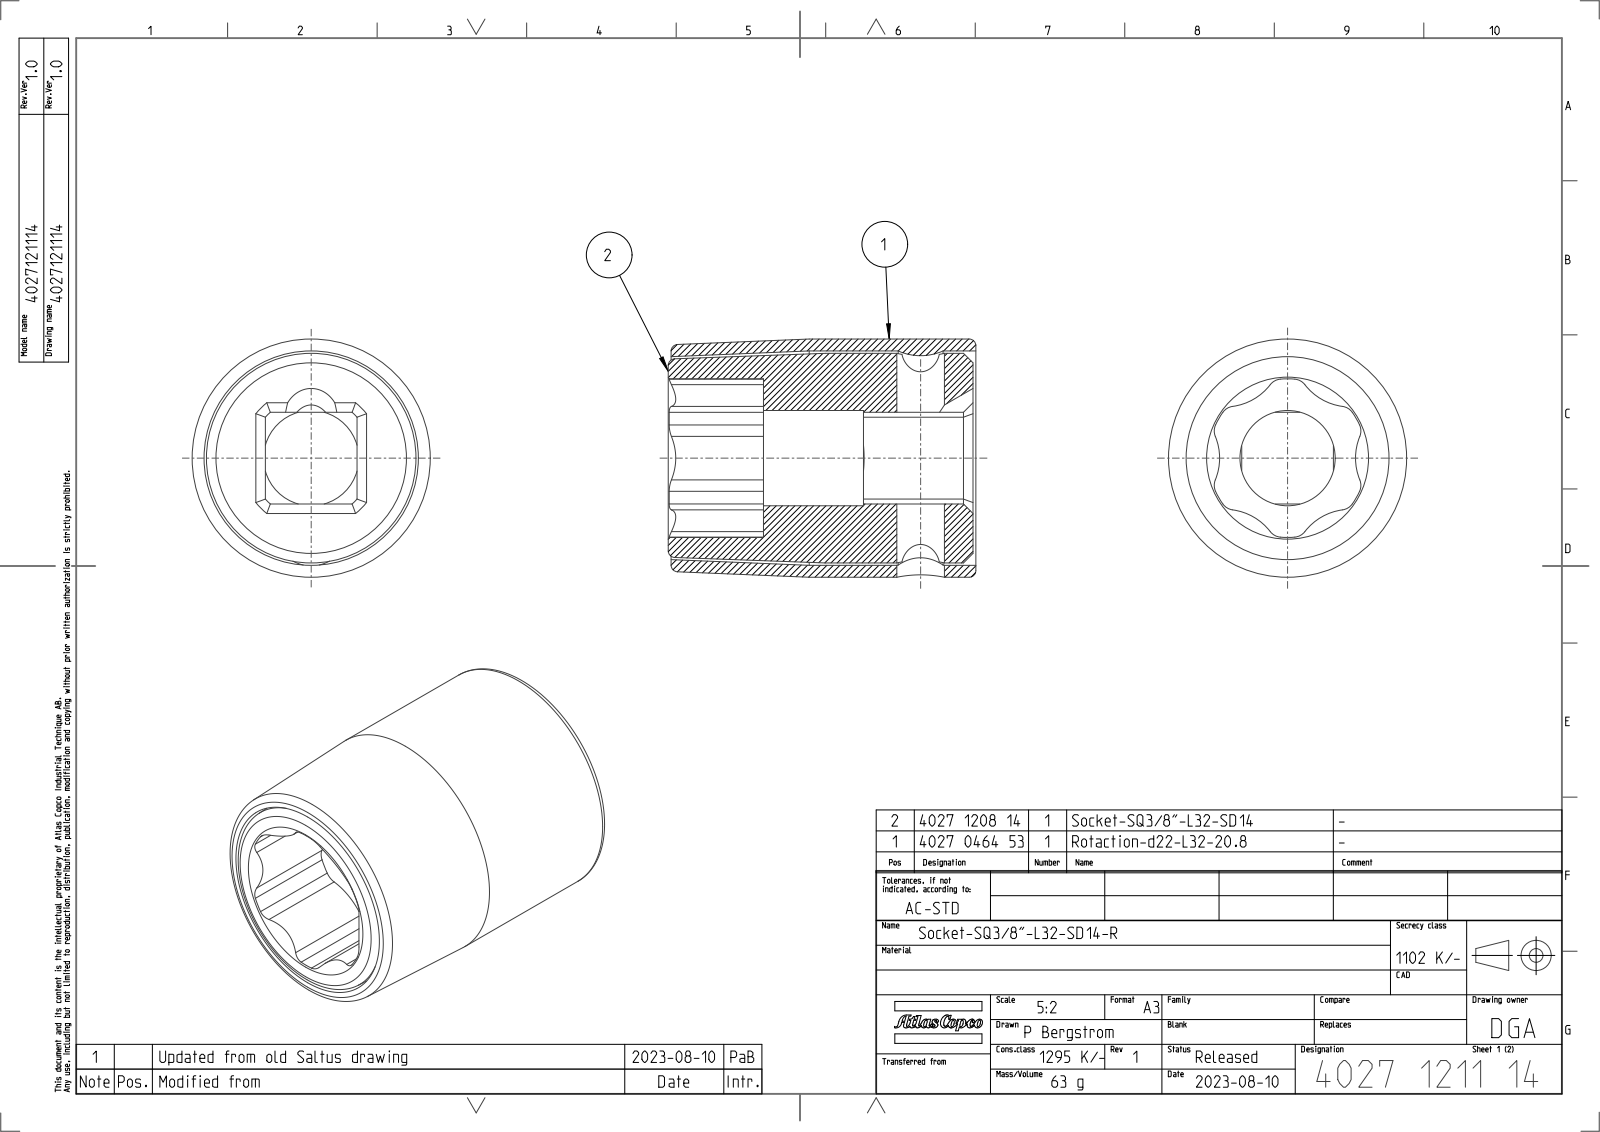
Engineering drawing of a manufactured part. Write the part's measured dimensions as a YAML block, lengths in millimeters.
part_name: "4027120814; 4027046453; 4027121114_ASM"
step_written_by: "CREO PARAMETRIC BY PTC INC, 2022414 (CONFIG_CONTROL_DESIGN)"
units: millimeters
bodies: {solids: 2, faces: 92, planar: 18, cylindrical: 47, other: 27}
overall_size: [32.3, 25, 25]
volume: 10470
surface_area: 8920
round_holes:
  - {diameter: 5, count: 1}
  - {diameter: 10, count: 1}
  - {diameter: 22.5, count: 1}
round_bosses_or_shafts:
  - {diameter: 25, count: 1}
  - {diameter: 22, count: 1}
partial_cylinders:
  - {radius: 1.5, count: 12}
  - {radius: 6, count: 6}
  - {radius: 3, count: 1}
  - {radius: 6.45, count: 1}
  - {radius: 8.32, count: 1}
face_to_face_distances: [9.62, 22, 32, 10, 22.3, 32.3, 31.7, 9.7, 11.8, 11.5]
